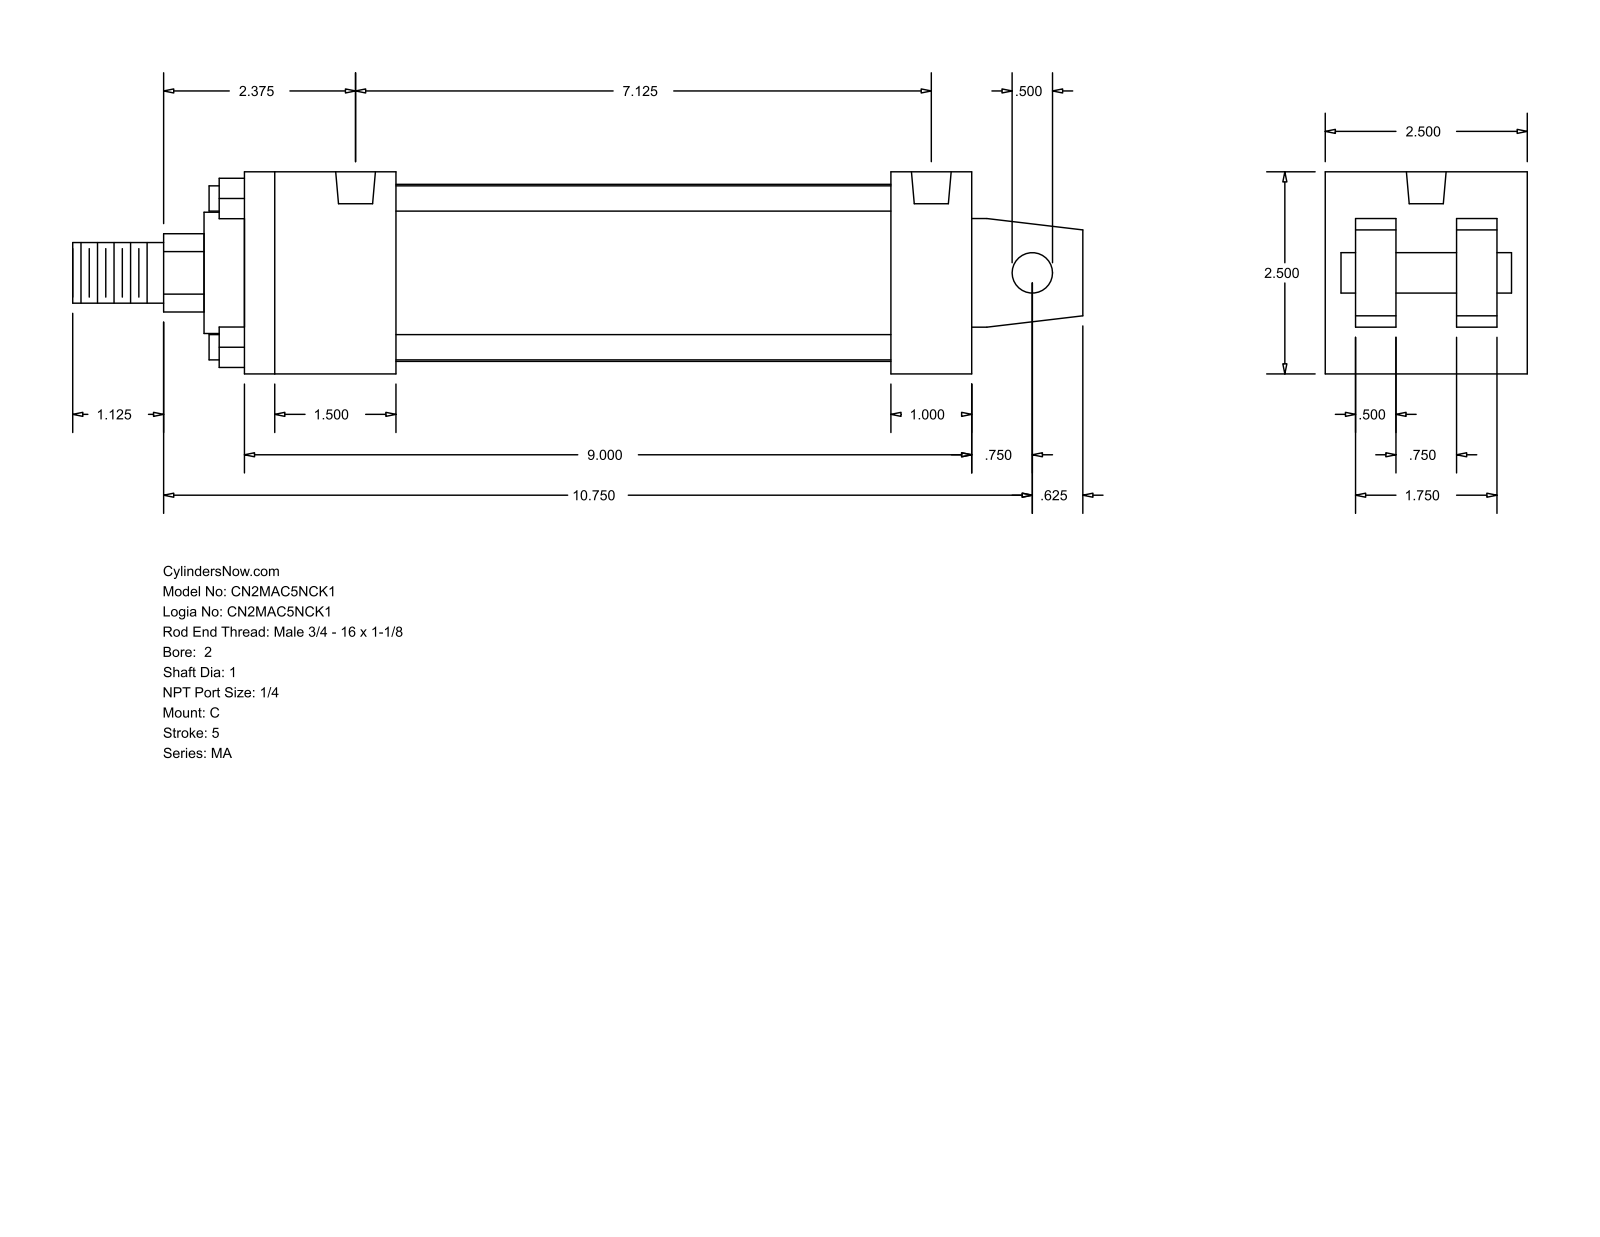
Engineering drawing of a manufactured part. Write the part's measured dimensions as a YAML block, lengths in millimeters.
part_name: "MA_C__0200_1"
step_written_by: "GSSL Pune (CONFIG_CONTROL_DESIGN)"
units: millimeters
bodies: {solids: 0, faces: 103, planar: 76, cylindrical: 27, other: 0}
overall_size: [317.5, 63.5, 63.5]
round_holes:
  - {diameter: 7.94, count: 4}
  - {diameter: 12.49, count: 2}
round_bosses_or_shafts:
  - {diameter: 7.94, count: 4}
  - {diameter: 55.63, count: 1}
  - {diameter: 38.1, count: 1}
  - {diameter: 25.4, count: 1}
  - {diameter: 19.05, count: 1}
  - {diameter: 12.7, count: 1}
partial_cylinders:
  - {radius: 12.29, count: 1}
face_to_face_distances: [63.5, 12.7, 228.6, 22.22, 41.28, 9.52, 53.98, 31.76, 47.63, 25.4]
hole_center_spacings: [180.97]
